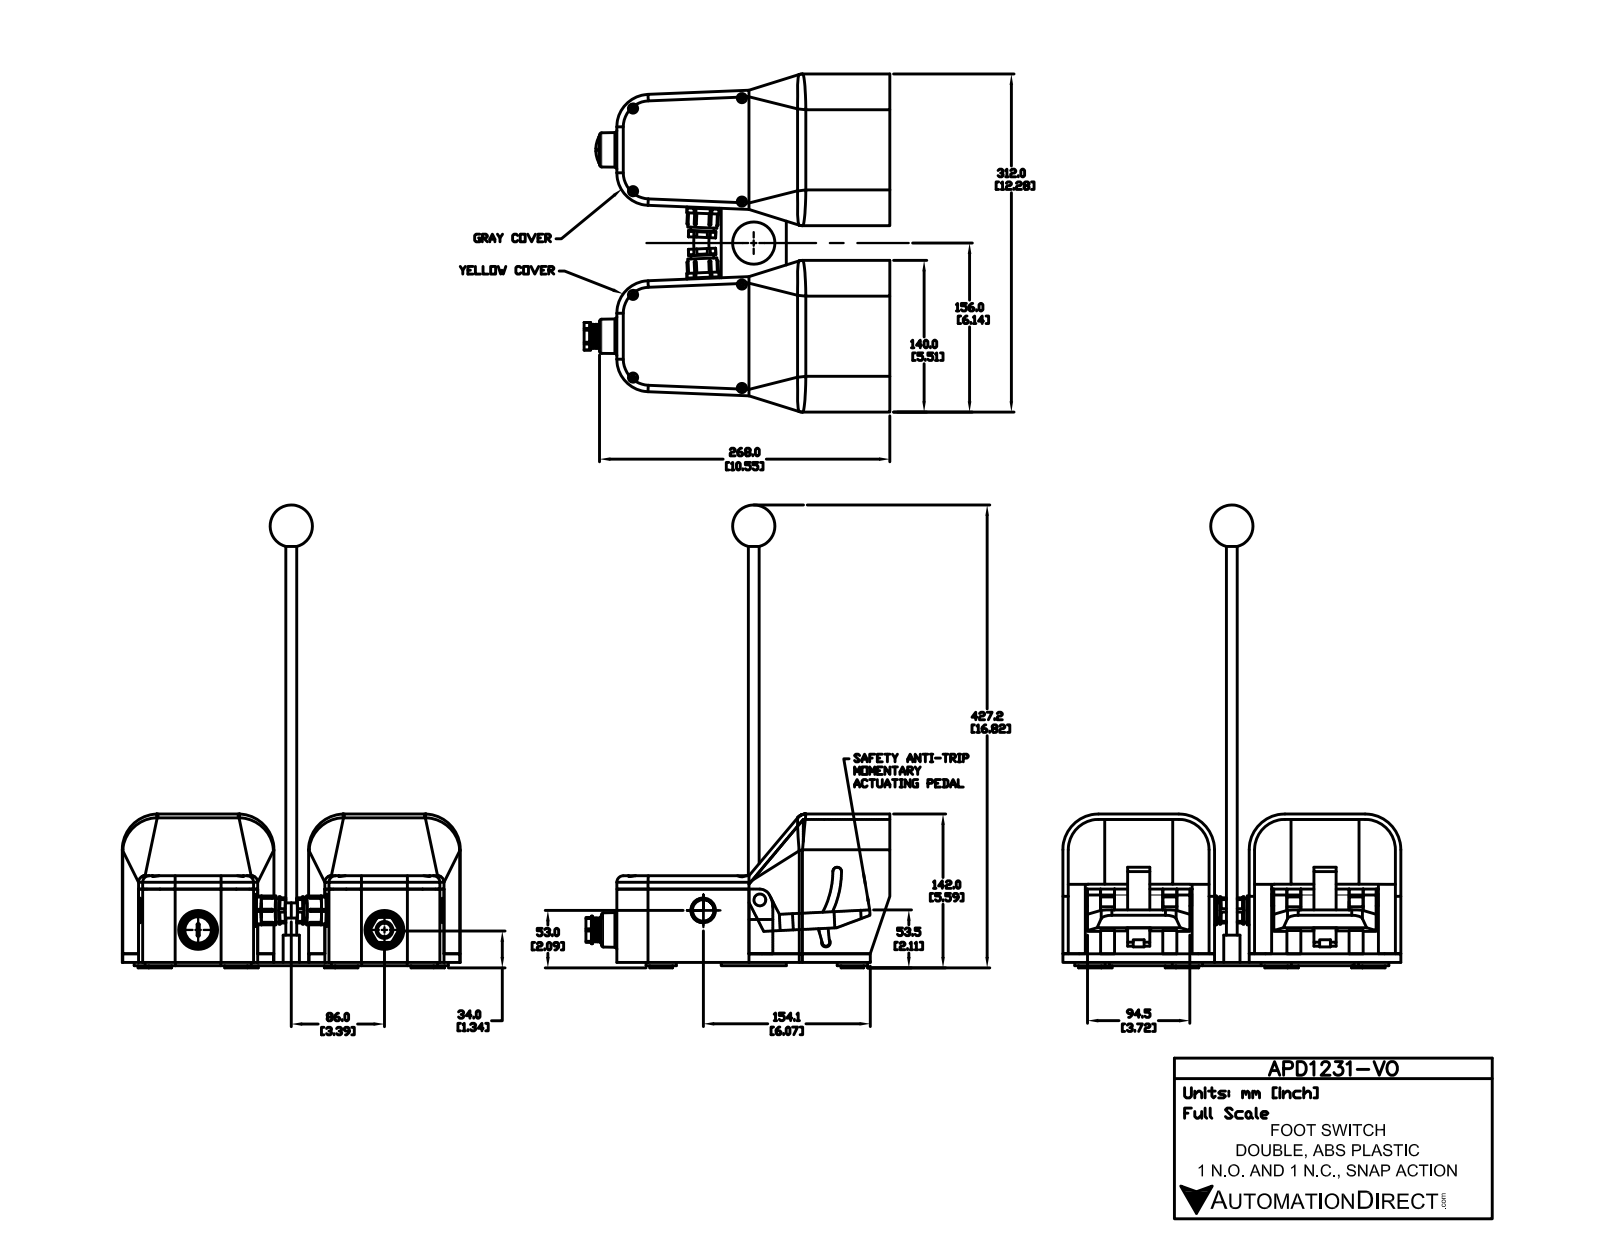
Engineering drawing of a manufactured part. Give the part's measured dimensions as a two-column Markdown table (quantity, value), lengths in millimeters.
| quantity | value |
| --- | --- |
| part name | APD1231-V0 |
| STEP written by | SolidWorks 2015 (AUTOMOTIVE_DESIGN) |
| units | millimeters |
| bodies | 38 solids, 865 faces (514 planar, 237 cylindrical, 114 other) |
| overall size | 427.2 × 312 × 282.2 |
| volume | 3 240 000 mm³ |
| surface area | 584 800 mm² |
| round holes (diameter × count) | 8.5 × 8, 22.8 × 4, 12.6 × 1, 15.6 × 1 |
| round bosses / shafts (diameter × count) | 28 × 8, 21 × 8, 19.9 × 4, 29.7 × 2, 26.7 × 2, 25.2 × 2, 21.5 × 2, 25.5 × 1 |
| partial cylindrical surfaces (radius × count) | 1 × 34, 1.1 × 12, 10 × 11, 6 × 5, 28 × 4, 30 × 4, 33 × 4, 20 × 2 |
| main face-to-face distances | 5, 135, 172, 8, 59.6, 140, 67.7, 59.7, 67.6, 3 |
| hole center spacings | 101, 132.2, 172, 76.3, 95.5, 132.4, 191, 207.6 |
